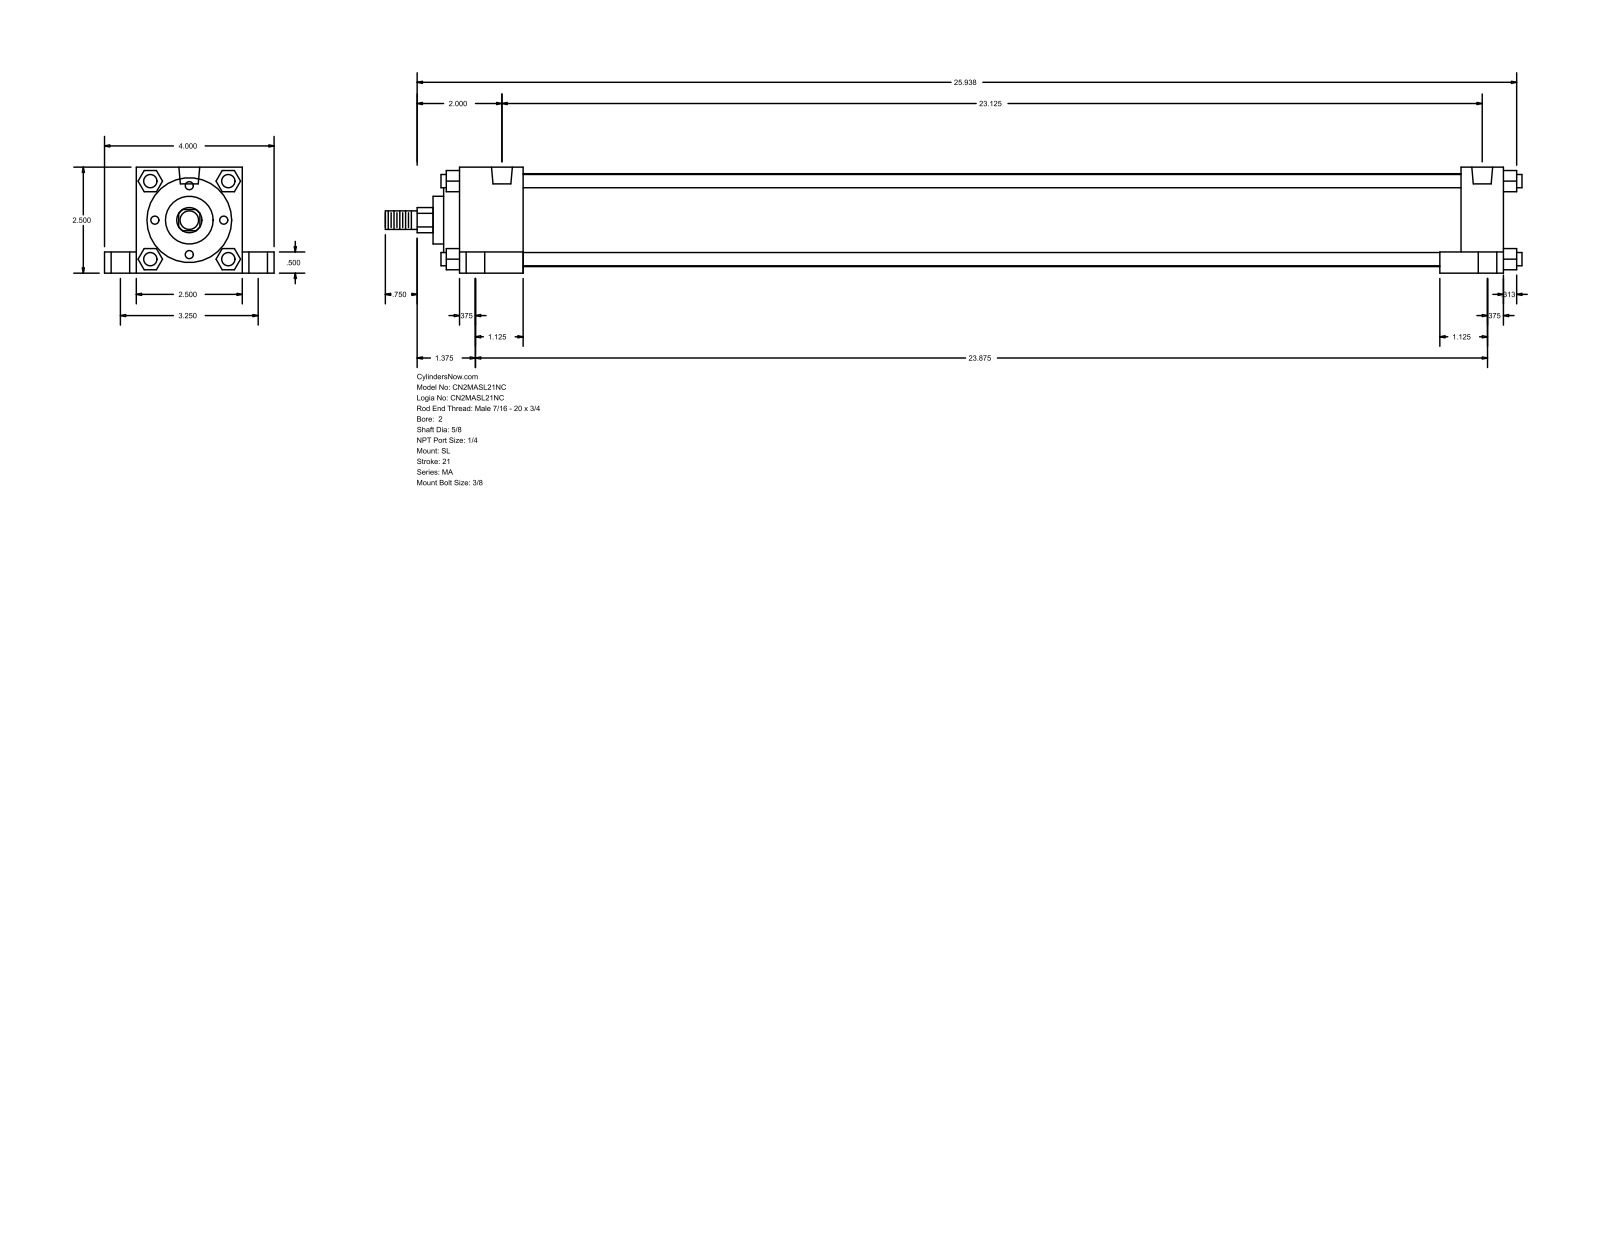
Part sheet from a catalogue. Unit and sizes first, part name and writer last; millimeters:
Units: millimetres
Overall size (bounding box): 681.04 × 101.6 × 63.5
Round holes (diameter × count): ⌀7.94 ×4, ⌀11.11 ×4, ⌀17.46 ×4, ⌀12.49 ×2
Round bosses / shafts (diameter × count): ⌀7.94 ×4, ⌀55.63 ×1, ⌀50.8 ×1, ⌀28.57 ×1, ⌀15.88 ×1, ⌀11.11 ×1
Partial cylindrical surfaces — rounded edges, fillets, slot ends (radius × count): R7.54 ×1
Main face-to-face distances: 63.5, 12.7, 9.52, 25.4, 19.05, 82.55, 38.1, 625.48, 50.8, 587.38
Hole centre spacings: 41.39, 44.22, 82.54, 587.37, 591.99, 604.66, 606.43, 612.02
Bodies: 0 solids, 150 faces (113 planar, 37 cylindrical, 0 other)
Part name (STEP PRODUCT): MA_SL__0200_0.625
STEP written by: GSSL Pune (CONFIG_CONTROL_DESIGN)
